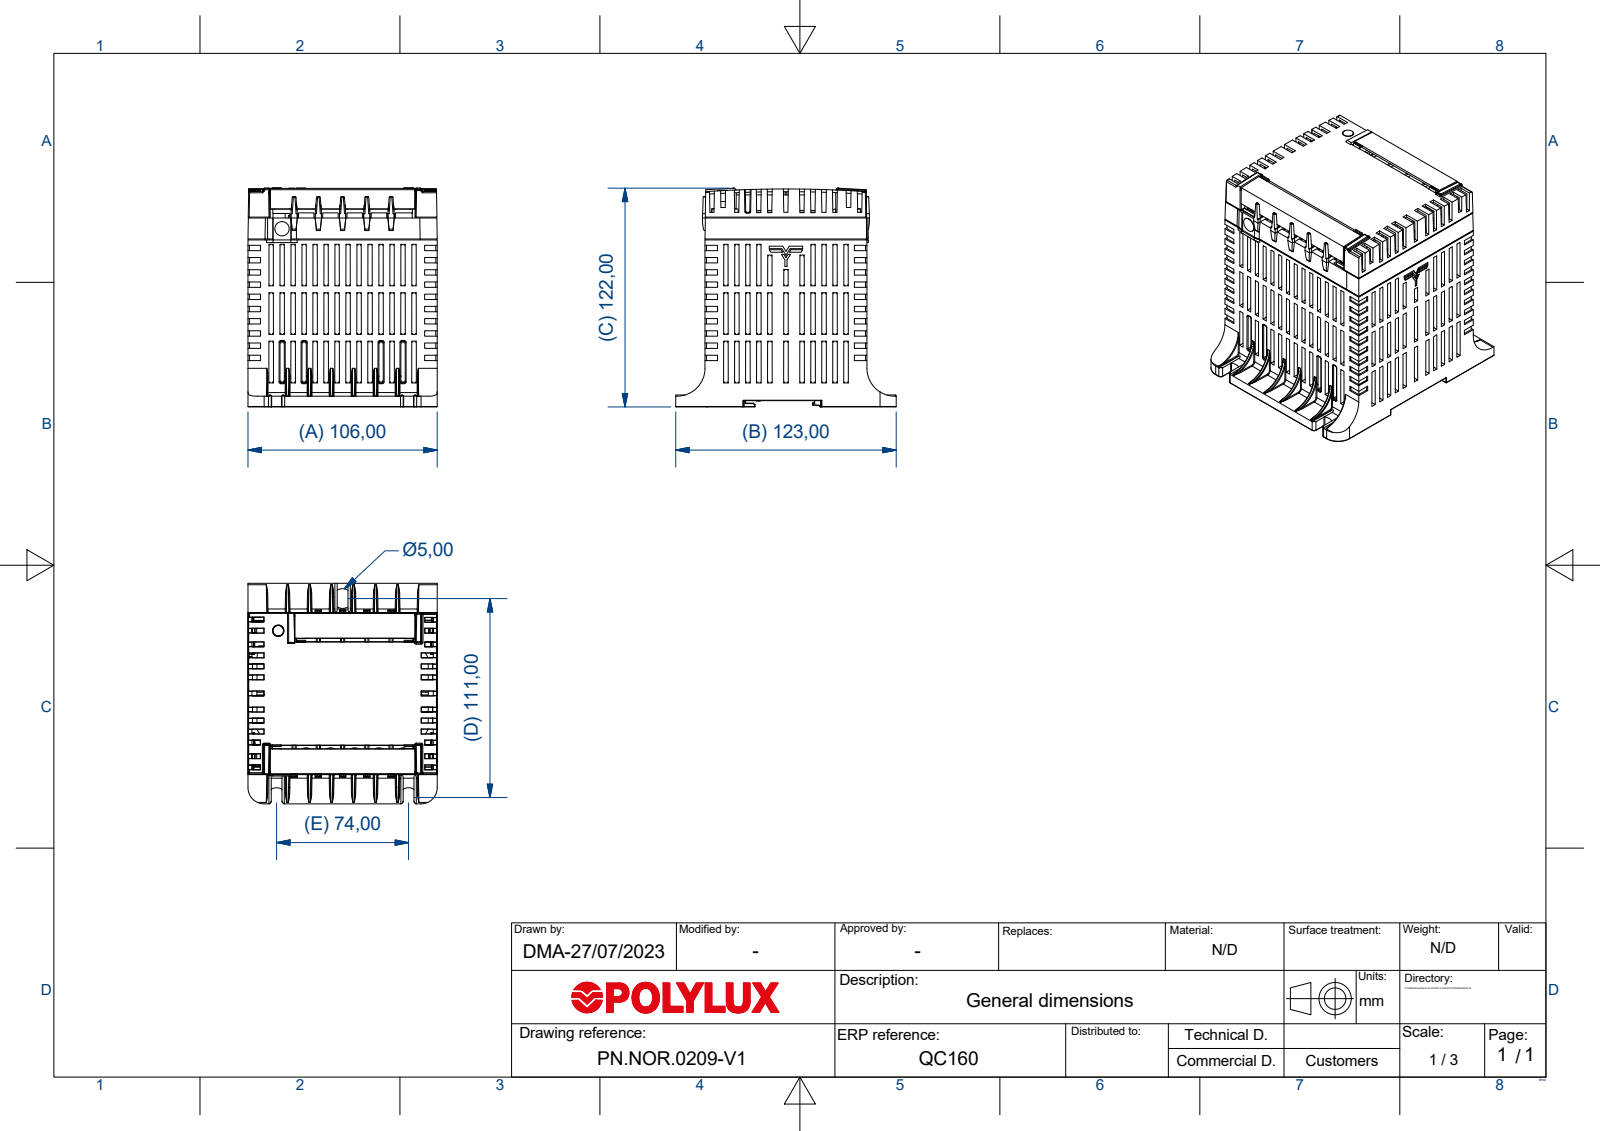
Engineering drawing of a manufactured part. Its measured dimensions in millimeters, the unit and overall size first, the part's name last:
Units: millimetres
Overall size (bounding box): 122.8 × 121.94 × 105.4
Round bosses / shafts (diameter × count): ⌀8 ×1
Partial cylindrical surfaces — rounded edges, fillets, slot ends (radius × count): R0.5 ×116, R0.25 ×87, R0.35 ×56, R0.71 ×26, R0.4 ×21, R0.3 ×15, R0.65 ×6, R31.25 ×6
Main face-to-face distances: 6.03, 2.5, 12.06, 12.05, 6.02, 105.4, 90.2, 18.09, 18.08, 24.11
Bodies: 0 solids, 3038 faces (1968 planar, 525 cylindrical, 545 other)
Part name (STEP PRODUCT): RC32
STEP written by: Autodesk Inventor 2018 (AUTOMOTIVE_DESIGN)
